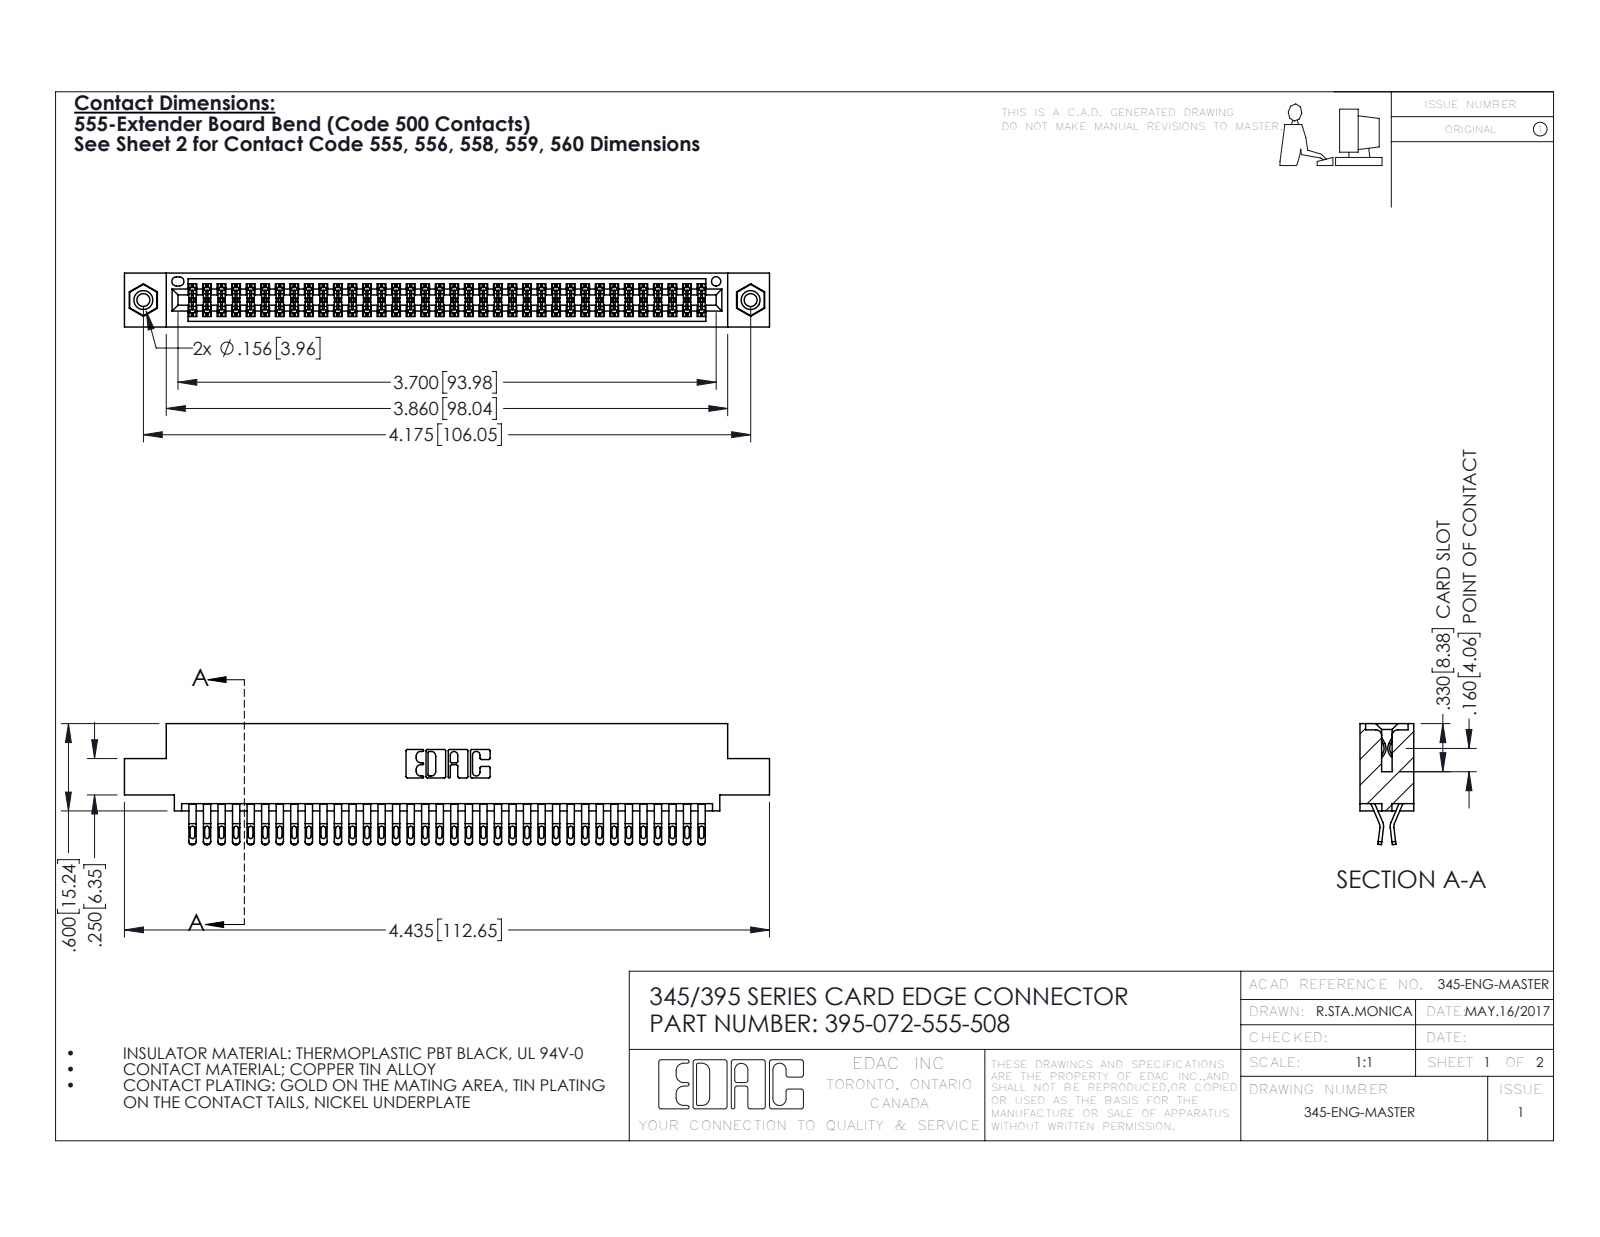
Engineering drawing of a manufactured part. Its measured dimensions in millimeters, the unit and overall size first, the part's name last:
Units: millimetres
Overall size (bounding box): 112.6 × 21.1 × 9.4
Round holes (diameter × count): ⌀2.3 ×2, ⌀3.2 ×2, ⌀4 ×2, ⌀1.6 ×1
Round bosses / shafts (diameter × count): ⌀3.9 ×2
Partial cylindrical surfaces — rounded edges, fillets, slot ends (radius × count): R0.4 ×180, R0.5 ×144, R0.2 ×108, R0.3 ×22, R0.2 ×6, R0.8 ×6, R0.7 ×3, R0.3 ×2
Main face-to-face distances: 1.8, 7.6, 0.6, 9.4, 5.1, 2.5, 6.9, 5.7, 4.4, 3.8
Hole centre spacings: 6.9, 100.1, 106
Volume: 11 000 mm³ · Surface area: 17 000 mm²
Bodies: 75 solids, 4222 faces (2348 planar, 1858 cylindrical, 16 other)
Part name (STEP PRODUCT): 395-072-555-508; 345-250-001_345-250-003-102; 345 Part_0.110 Offset - 0.156 Dia-TI; 345-292-001_555 Tail
STEP written by: SolidWorks 2016 (CONFIG_CONTROL_DESIGN)
